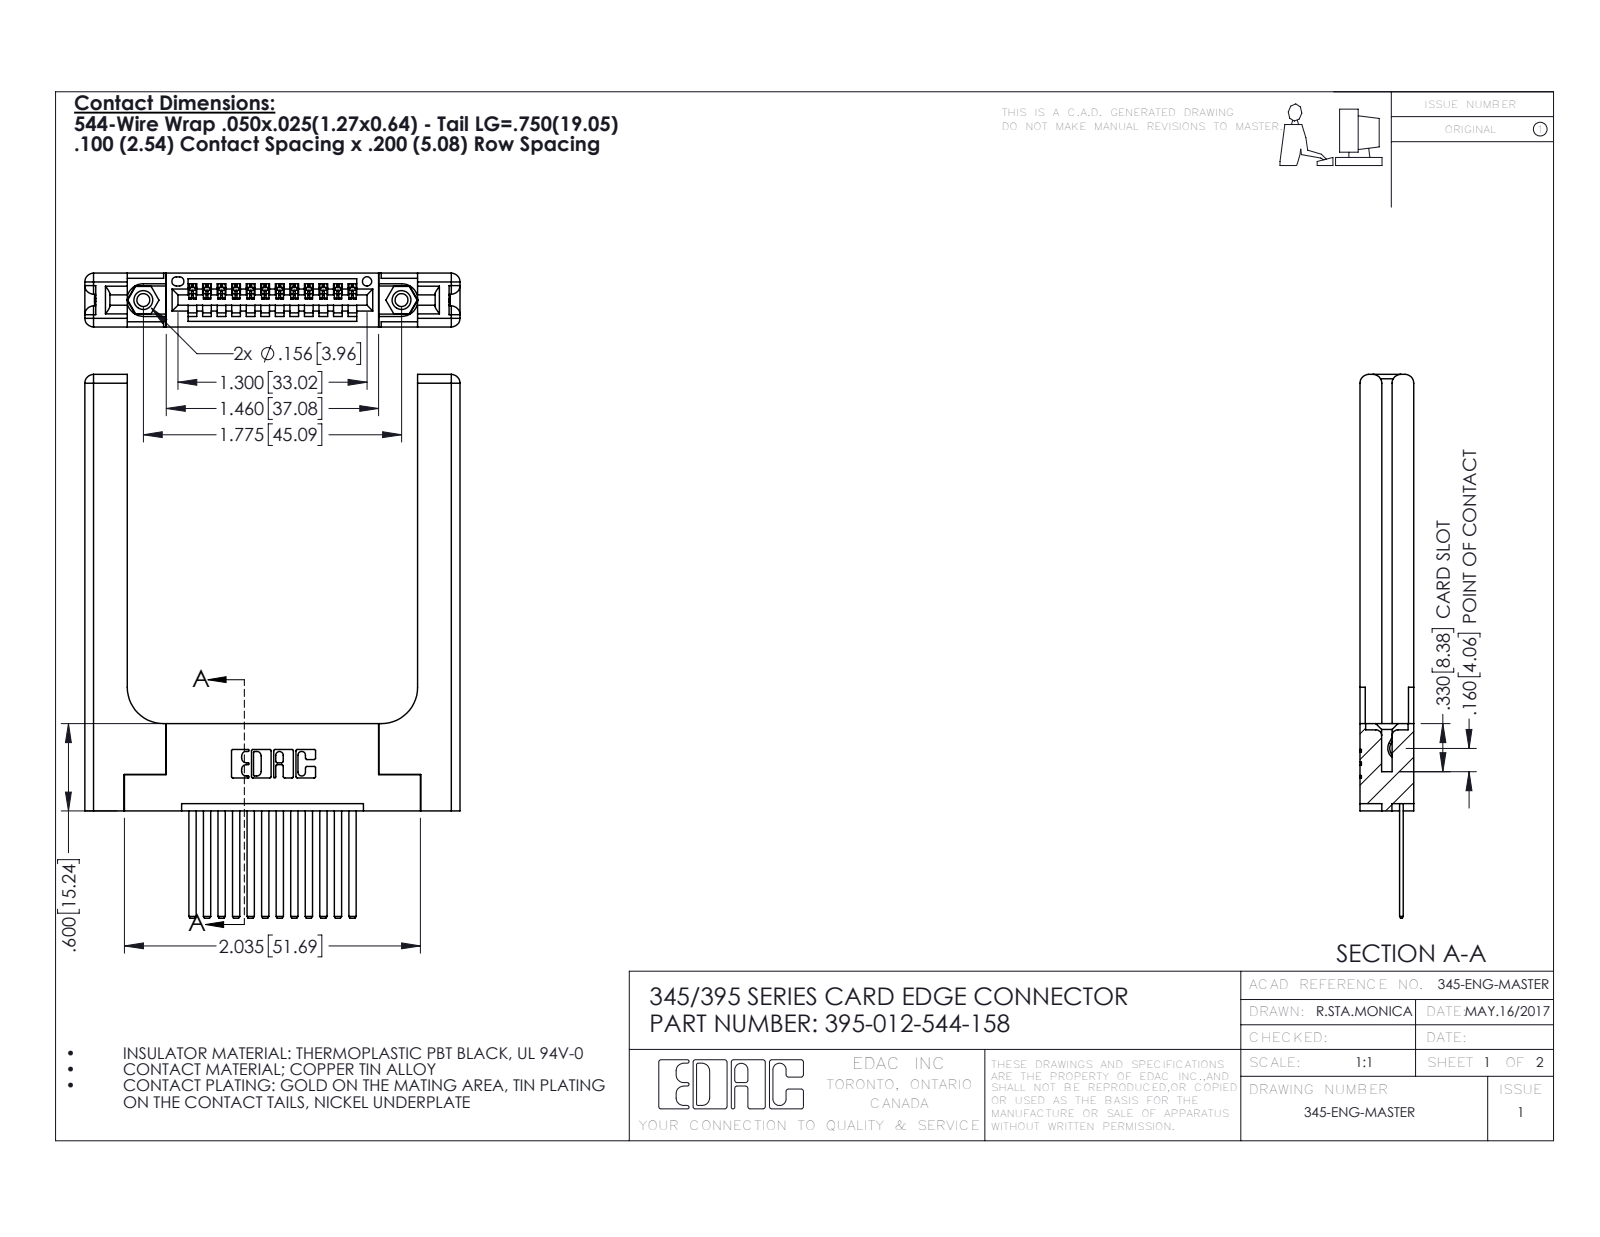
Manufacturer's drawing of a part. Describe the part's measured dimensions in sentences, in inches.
The part is named "345-220-058_345-220-058; 345 Part_Flush Mounting Lugs - 0.156 Dia-TH; 395-012-544-158; 345-292-001_345-293-144 (+1 more)". Its 3-D file was written by "SolidWorks 2016 (CONFIG_CONTROL_DESIGN)". It is 17 solids with 1006 faces: 660 planar, 286 cylindrical and 60 other. Overall it measures 3.737 by 2.579 by 0.37 inches. Its volume is 0.892 cubic inches and its surface area 20.83 square inches. Round holes: 2 of diameter 0.089, 2 of diameter 0.125, 2 of diameter 0.156, 1 of diameter 0.064. Round bosses or shafts: 2 of diameter 0.155. Partial cylindrical surfaces (rounded edges, fillets, slot ends): 24 of radius 0.006, 22 of radius 0.01, 16 of radius 0.06, 6 of radius 0.007, 6 of radius 0.031, 3 of radius 0.026, 2 of radius 0.03, 2 of radius 0.031. The main face-to-face distances are 0.37, 0.072, 0.298, 0.15, 0.22, 0.077, 0.148, 0.2, 0.098, 0.272. The hole center spacings are 0.27, 1.543, 1.775.
